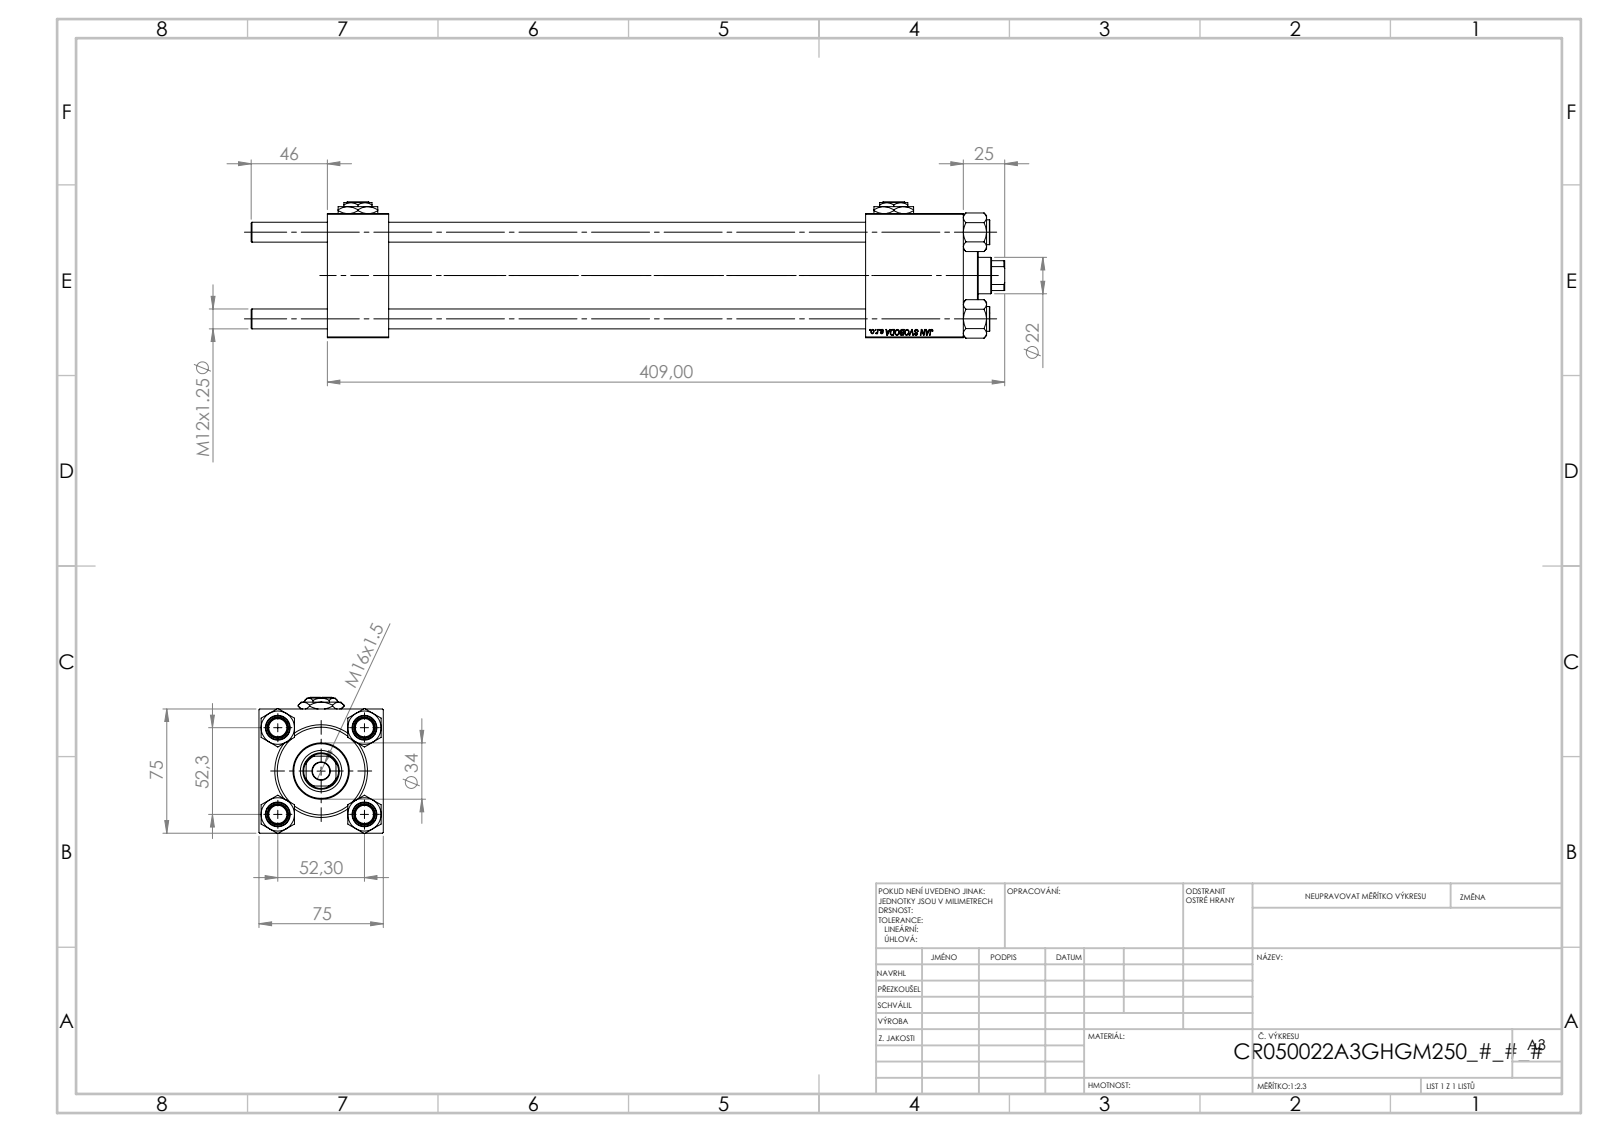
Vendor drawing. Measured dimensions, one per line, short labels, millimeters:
name: CR025_012_A_0_G_A_G_M_020_+#_##_TYCINKA; V215_VC_A; V215CR_BODY_A; NUT_M5 (+2 more)
written by: SolidWorks 2019 (CONFIG_CONTROL_DESIGN)
unit: mm
bodies: 13 solids, 1233 faces (567 planar, 88 cylindrical, 578 other)
size: 455 × 82.27 × 75
volume: 991 331 mm³; area: 295 391 mm²
holes: 4× ⌀12, 2× ⌀7, 2× ⌀20.96, 2× ⌀30, 1× ⌀10.5, 1× ⌀22, 1× ⌀25, 1× ⌀41, 1× ⌀50, 1× ⌀53
bosses: 4× ⌀15, 1× ⌀56, 1× ⌀34
rounds: 1× R10.5
face distances: 75, 37, 384, 347, 325, 59, 288, 355.3, 318.3, 30.3
hole spacings: 36.98, 52.3, 73.96, 323.5
